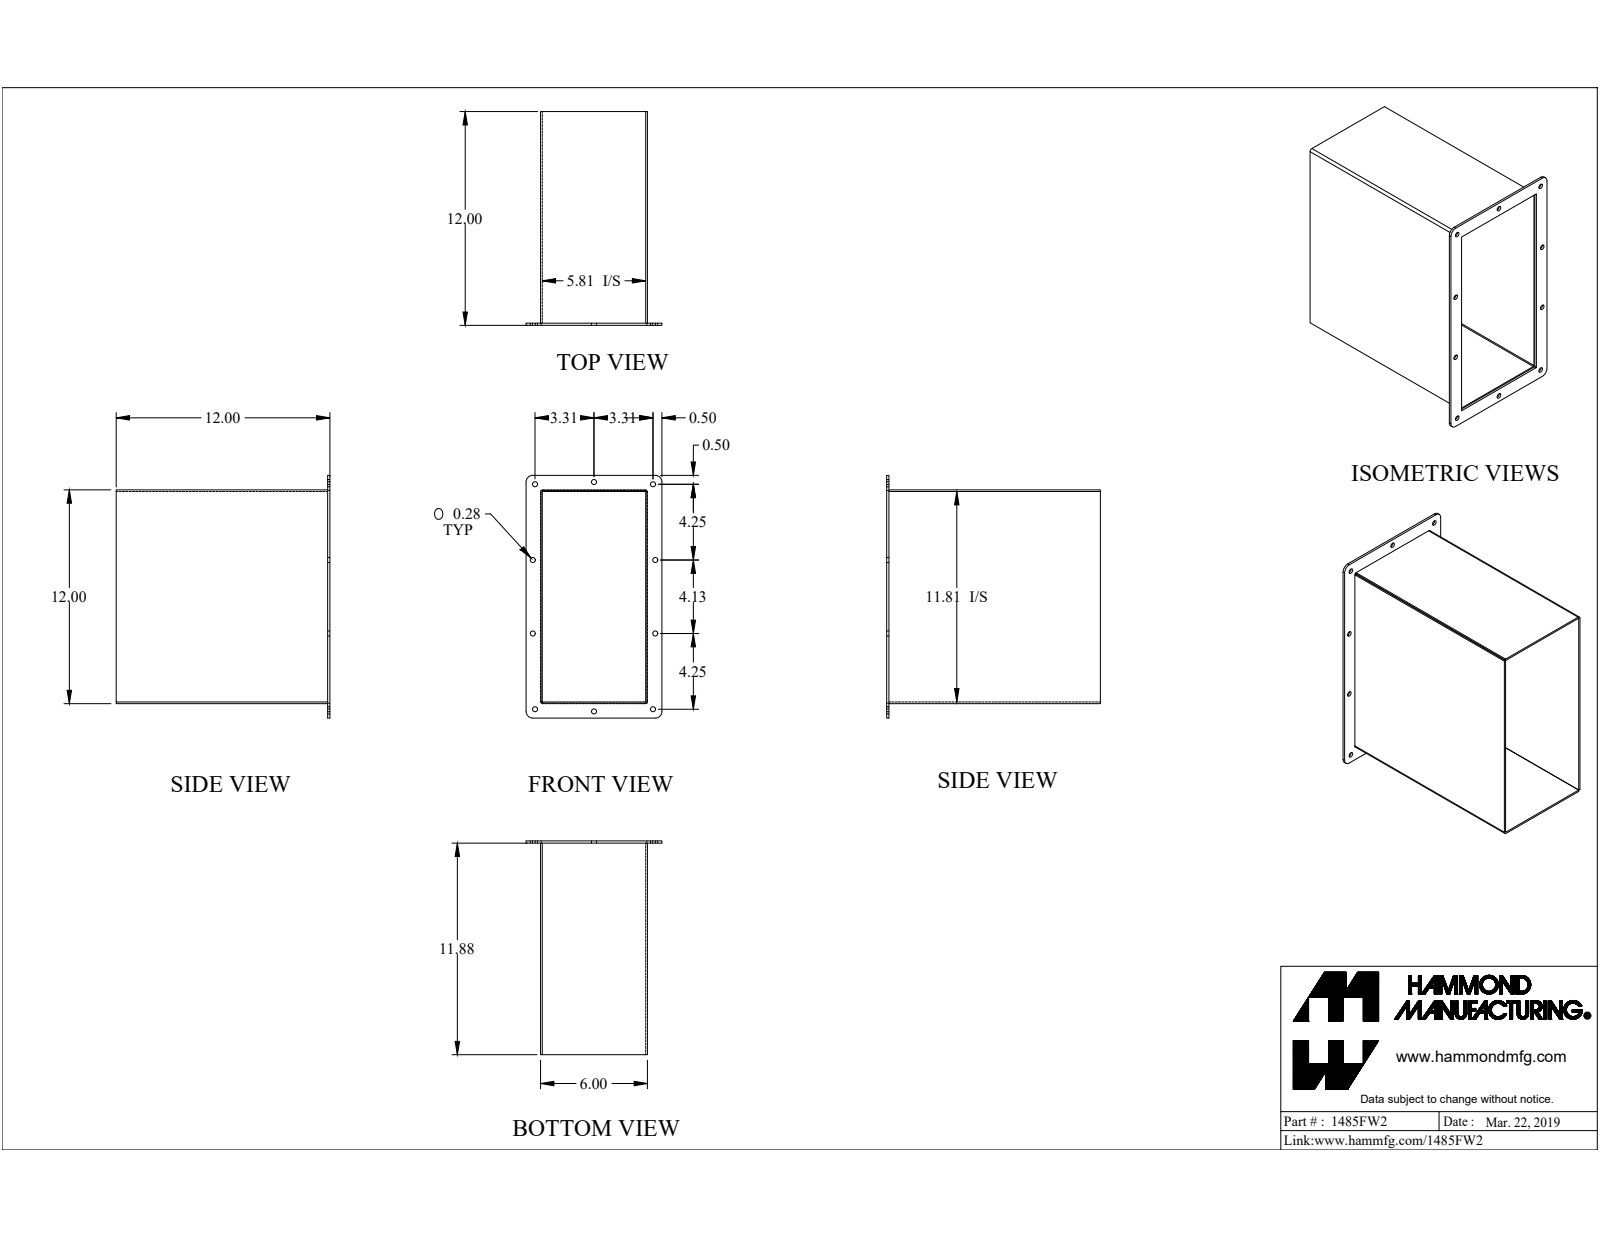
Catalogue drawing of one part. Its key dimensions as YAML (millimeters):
part_name: "1485FW2"
step_written_by: "SolidWorks 2019 (CONFIG_CONTROL_DESIGN)"
units: millimeters
bodies: {solids: 4, faces: 68, planar: 36, cylindrical: 32, other: 0}
overall_size: [346.1, 308, 193.7]
volume: 785600
surface_area: 645800
round_holes:
  - {diameter: 7.1, count: 10}
partial_cylinders:
  - {radius: 9.5, count: 4}
  - {radius: 1.2, count: 2}
  - {radius: 3.6, count: 2}
face_to_face_distances: [2.4, 150, 147.6, 152.4, 302.4, 304.8, 300, 3.2, 301.6, 308]
hole_center_spacings: [84.2, 108, 141.3, 202.6, 212.8, 232.9, 273.2, 334.6]
